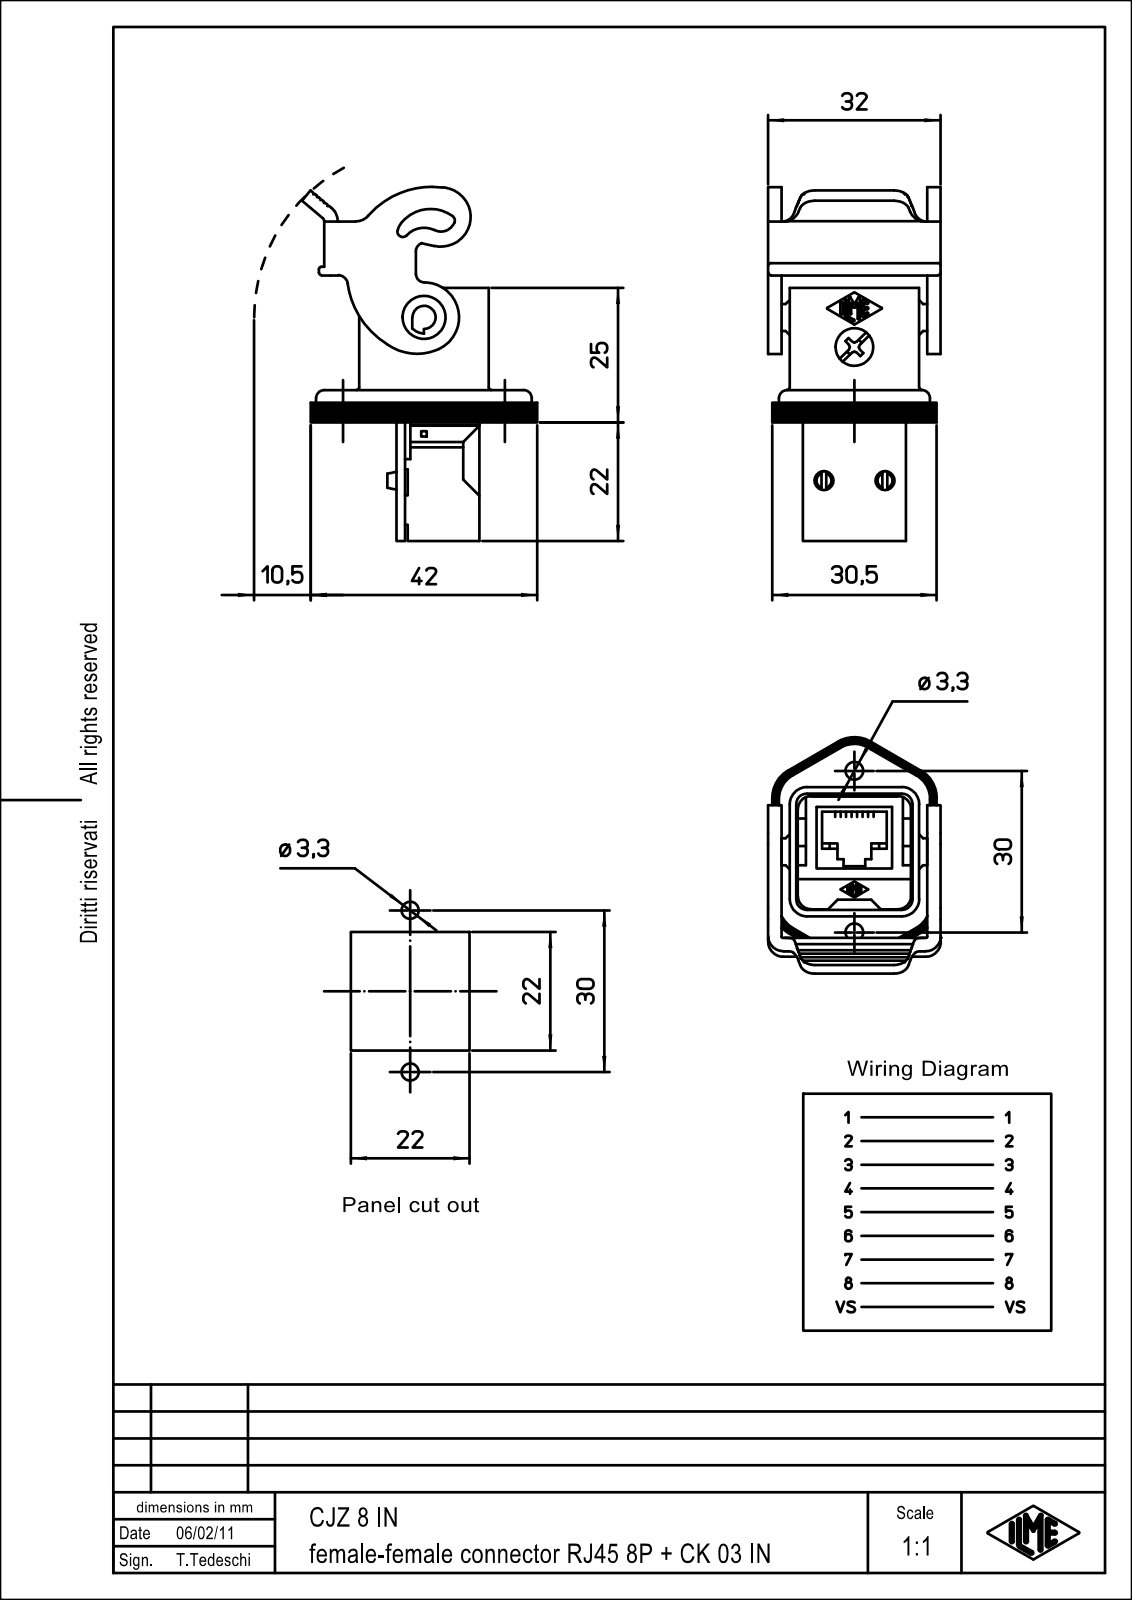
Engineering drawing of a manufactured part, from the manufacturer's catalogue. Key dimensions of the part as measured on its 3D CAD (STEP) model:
Part name (STEP PRODUCT): CJZ_8_IN
STEP written by: PTC Creo Elements/Direct Modeling 19.0E 27-Jun-2016 (C) Parametric Technology GmbH (AUTOMOTIVE_DESIGN)
Units: millimetres
Bodies: 1 solid, 388 faces (246 planar, 119 cylindrical, 23 other)
Overall size (bounding box): 65.33 × 44.15 × 32
Volume: 20 280 mm³ · Surface area: 16 928 mm²
Round holes (diameter × count): ⌀3.3 ×2, ⌀3.3 ×2, ⌀3.5 ×2, ⌀4.2 ×1, ⌀8 ×1
Round bosses / shafts (diameter × count): ⌀3.4 ×4, ⌀5.6 ×1, ⌀5 ×1, ⌀4 ×1
Partial cylindrical surfaces — rounded edges, fillets, slot ends (radius × count): R2 ×13, R3 ×12, R1.75 ×8, R0.5 ×7, R1 ×6, R1.5 ×6, R2.4 ×4, R20 ×2
Main face-to-face distances: 24, 21.5, 2.75, 2.5, 1.25, 22.75, 4, 29.5, 8, 5.5
Hole centre spacings: 11.3, 30
